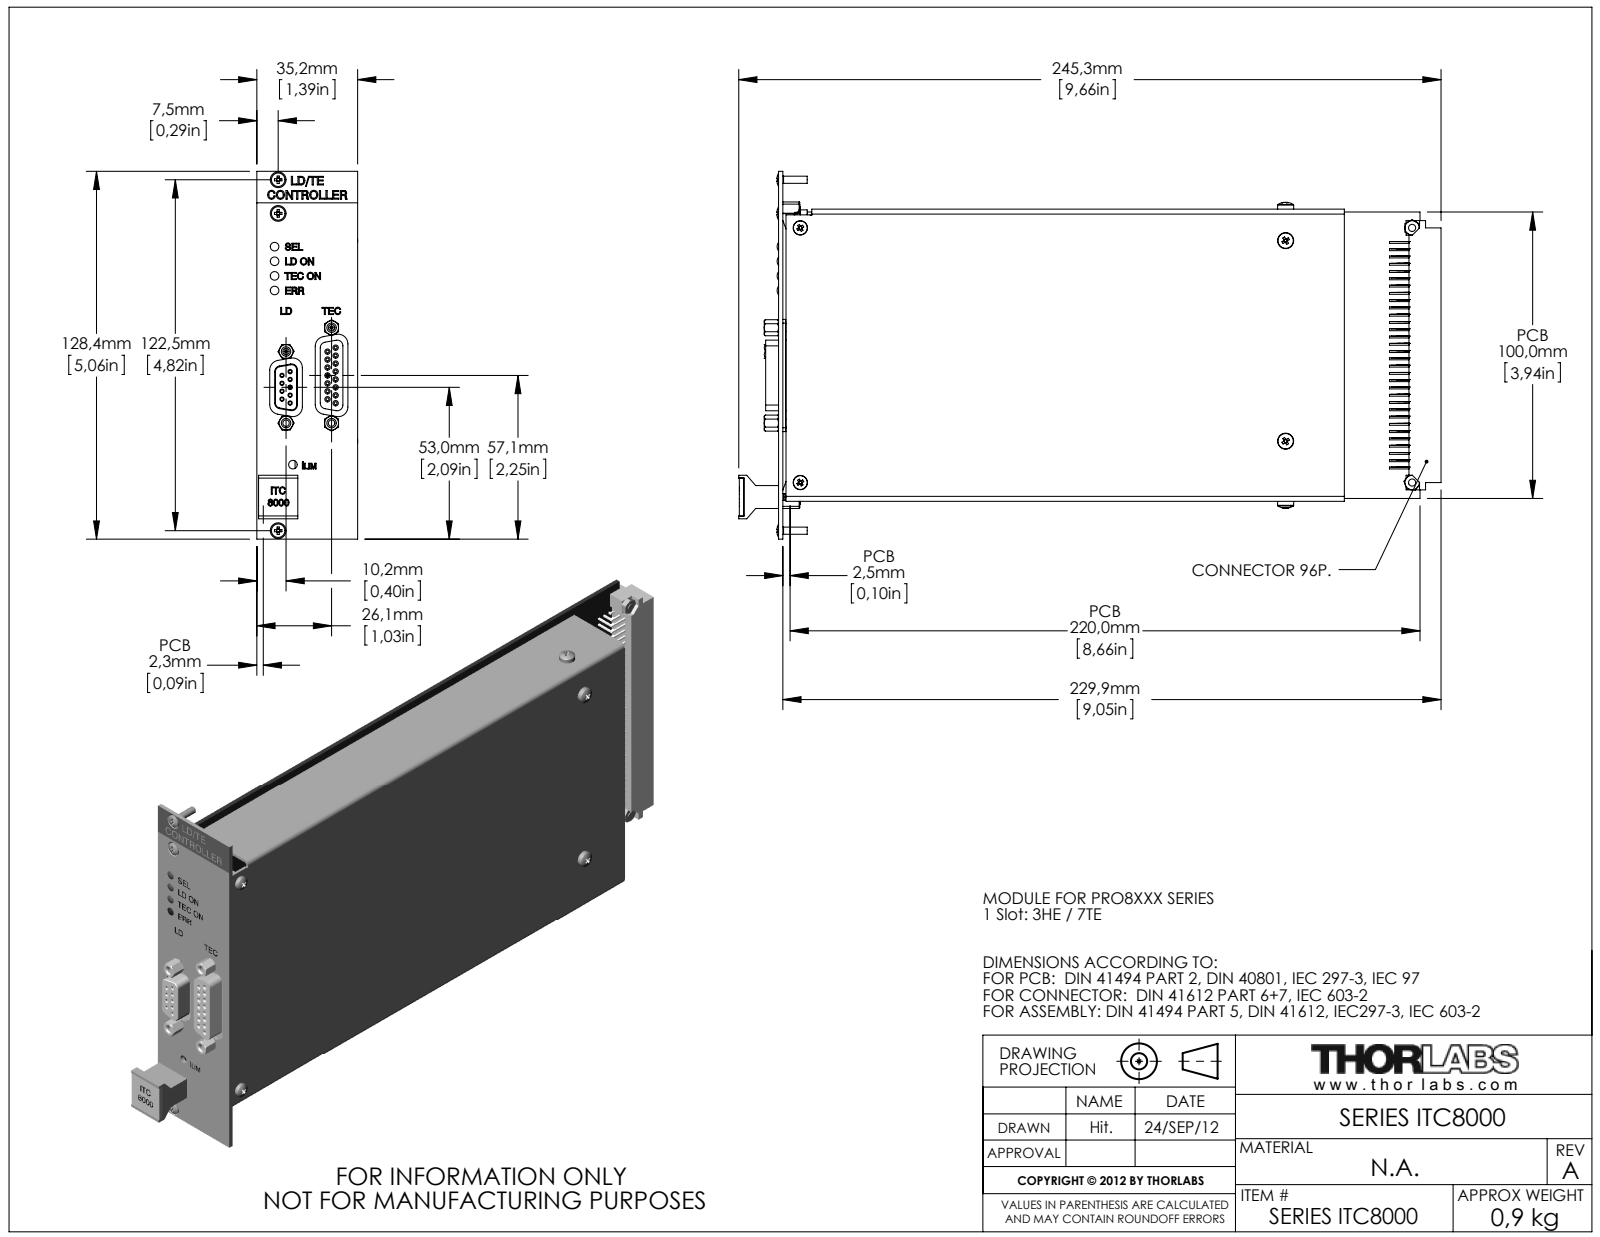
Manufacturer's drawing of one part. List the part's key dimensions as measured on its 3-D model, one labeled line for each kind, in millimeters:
Part name (STEP PRODUCT): 7225-E0W; DSUB9-F; Vorlage einschub ohne Front; ISO 7045 - M3 x 6 - Z --- 6N (+8 more)
STEP written by: SolidWorks 2012 (CONFIG_CONTROL_DESIGN)
Units: millimetres
Bodies: 132 solids, 3309 faces (2341 planar, 330 cylindrical, 638 other)
Overall size (bounding box): 245.27 × 128.4 × 35.2
Volume: 84 296 mm³ · Surface area: 129 074 mm²
Round holes (diameter × count): ⌀1 ×24, ⌀2.7 ×10, ⌀2.05 ×6, ⌀3 ×5, ⌀3.2 ×5, ⌀2.26 ×4, ⌀2.5 ×4, ⌀3.1 ×4, ⌀2.6 ×2, ⌀2.8 ×2, ⌀3.05 ×2, ⌀5.5 ×1
Round bosses / shafts (diameter × count): ⌀5 ×5, ⌀2.7 ×4, ⌀2.5 ×4, ⌀5.6 ×3, ⌀4.7 ×3, ⌀3 ×3, ⌀2.4 ×2
Partial cylindrical surfaces — rounded edges, fillets, slot ends (radius × count): R0.2 ×39, R0.5 ×12, R1.5 ×9, R2 ×9, R3.4 ×8, R1 ×6, R1.3 ×4, R0.74 ×2
Main face-to-face distances: 1, 1.6, 30.6, 29, 29.6, 28, 101, 1.5, 100, 102
Hole centre spacings: 3.16, 2.77, 5.54, 8.31, 11.08, 5.03, 5.04, 7.48
